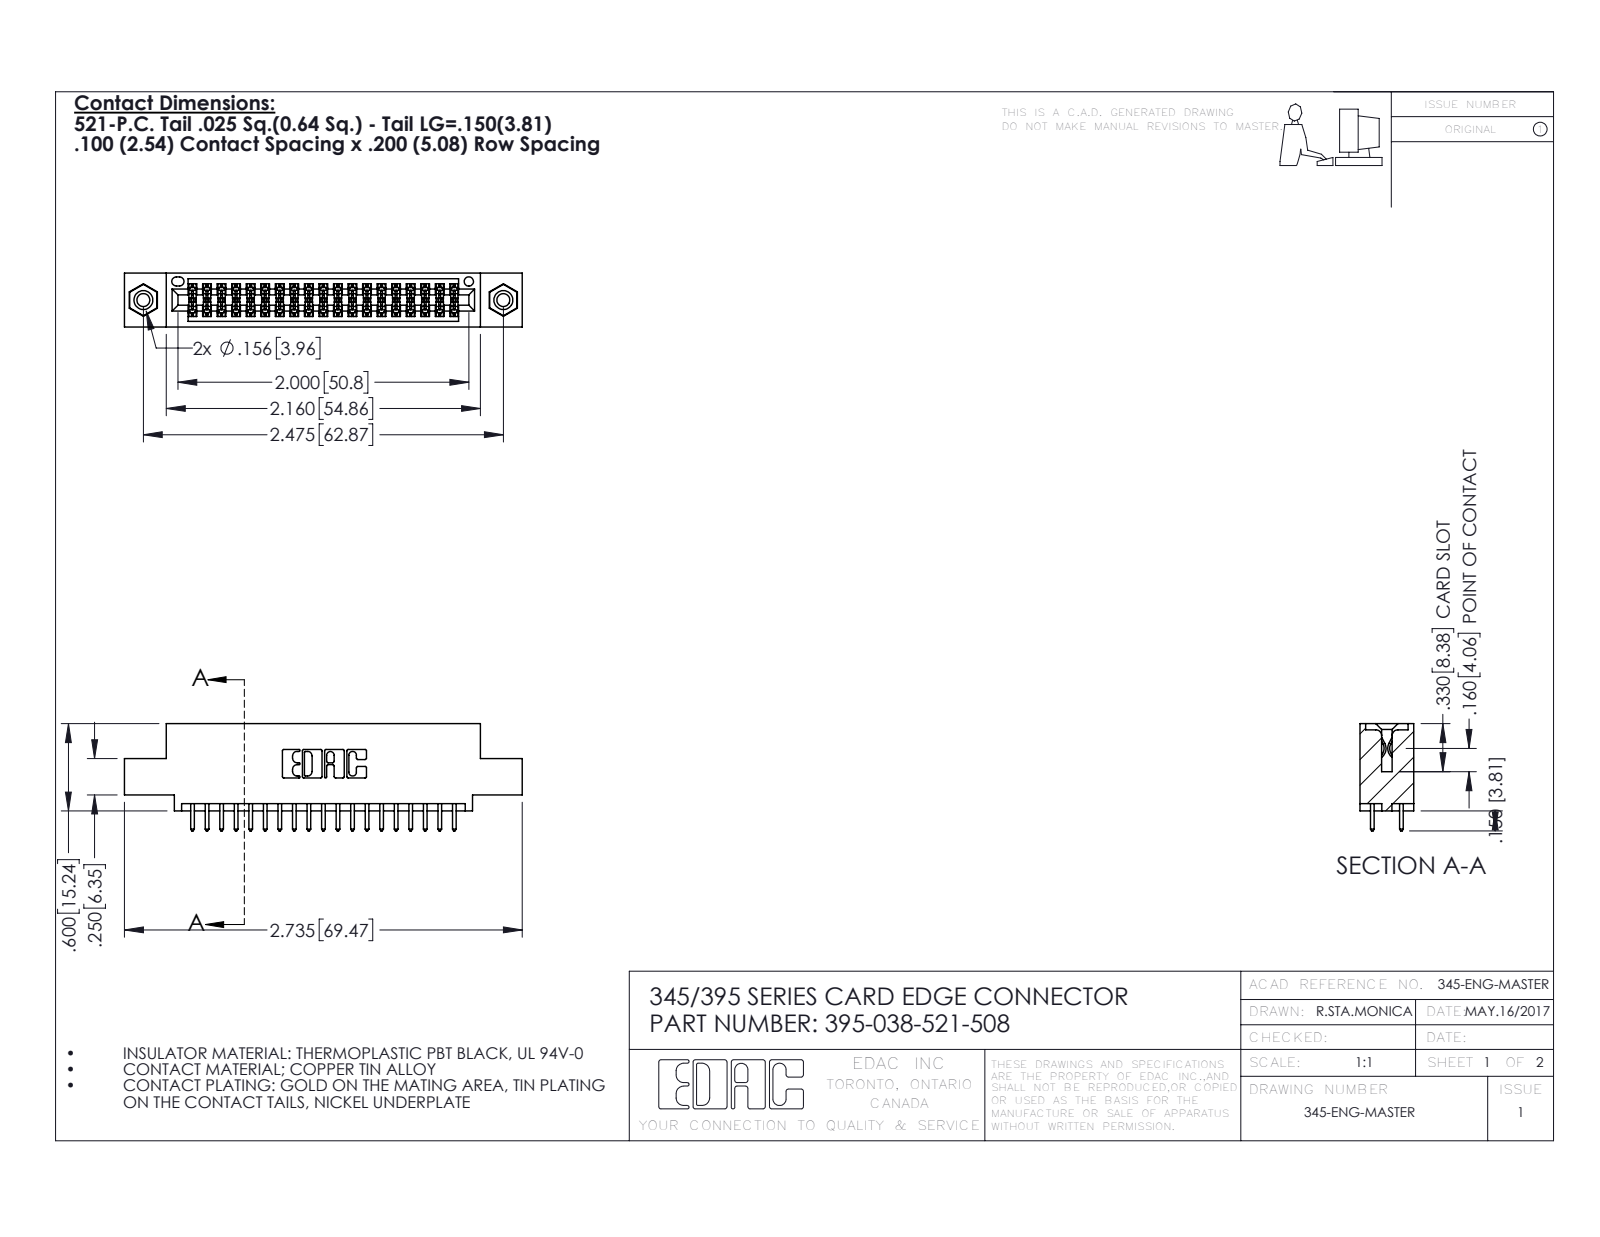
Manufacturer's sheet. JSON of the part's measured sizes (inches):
{"part_name": "345-292-001_345-293-121; 395-038-521-508; 345-250-001_345-250-003-102; 345 Part_0.110 Offset - 0.156 Dia-TI", "step_written_by": "SolidWorks 2016 (CONFIG_CONTROL_DESIGN)", "units": "inches", "bodies": {"solids": 41, "faces": 2090, "planar": 1370, "cylindrical": 704, "other": 16}, "overall_size": [2.735, 0.737, 0.37], "volume_in3": 0.393, "surface_area_in2": 14.07, "round_holes": [[0.089, 2], [0.125, 2], [0.156, 2], [0.064, 1]], "round_bosses_or_shafts": [[0.155, 2]], "partial_cylinders_radius": [[0.006, 57], [0.01, 38], [0.01, 22], [0.007, 6], [0.031, 6], [0.026, 3], [0.014, 2], [0.019, 2]], "face_to_face_distances": [0.072, 0.298, 0.2, 0.37, 0.098, 0.272, 0.025, 0.225, 0.175, 0.149], "hole_center_spacings": [0.27, 2.241, 2.475]}
